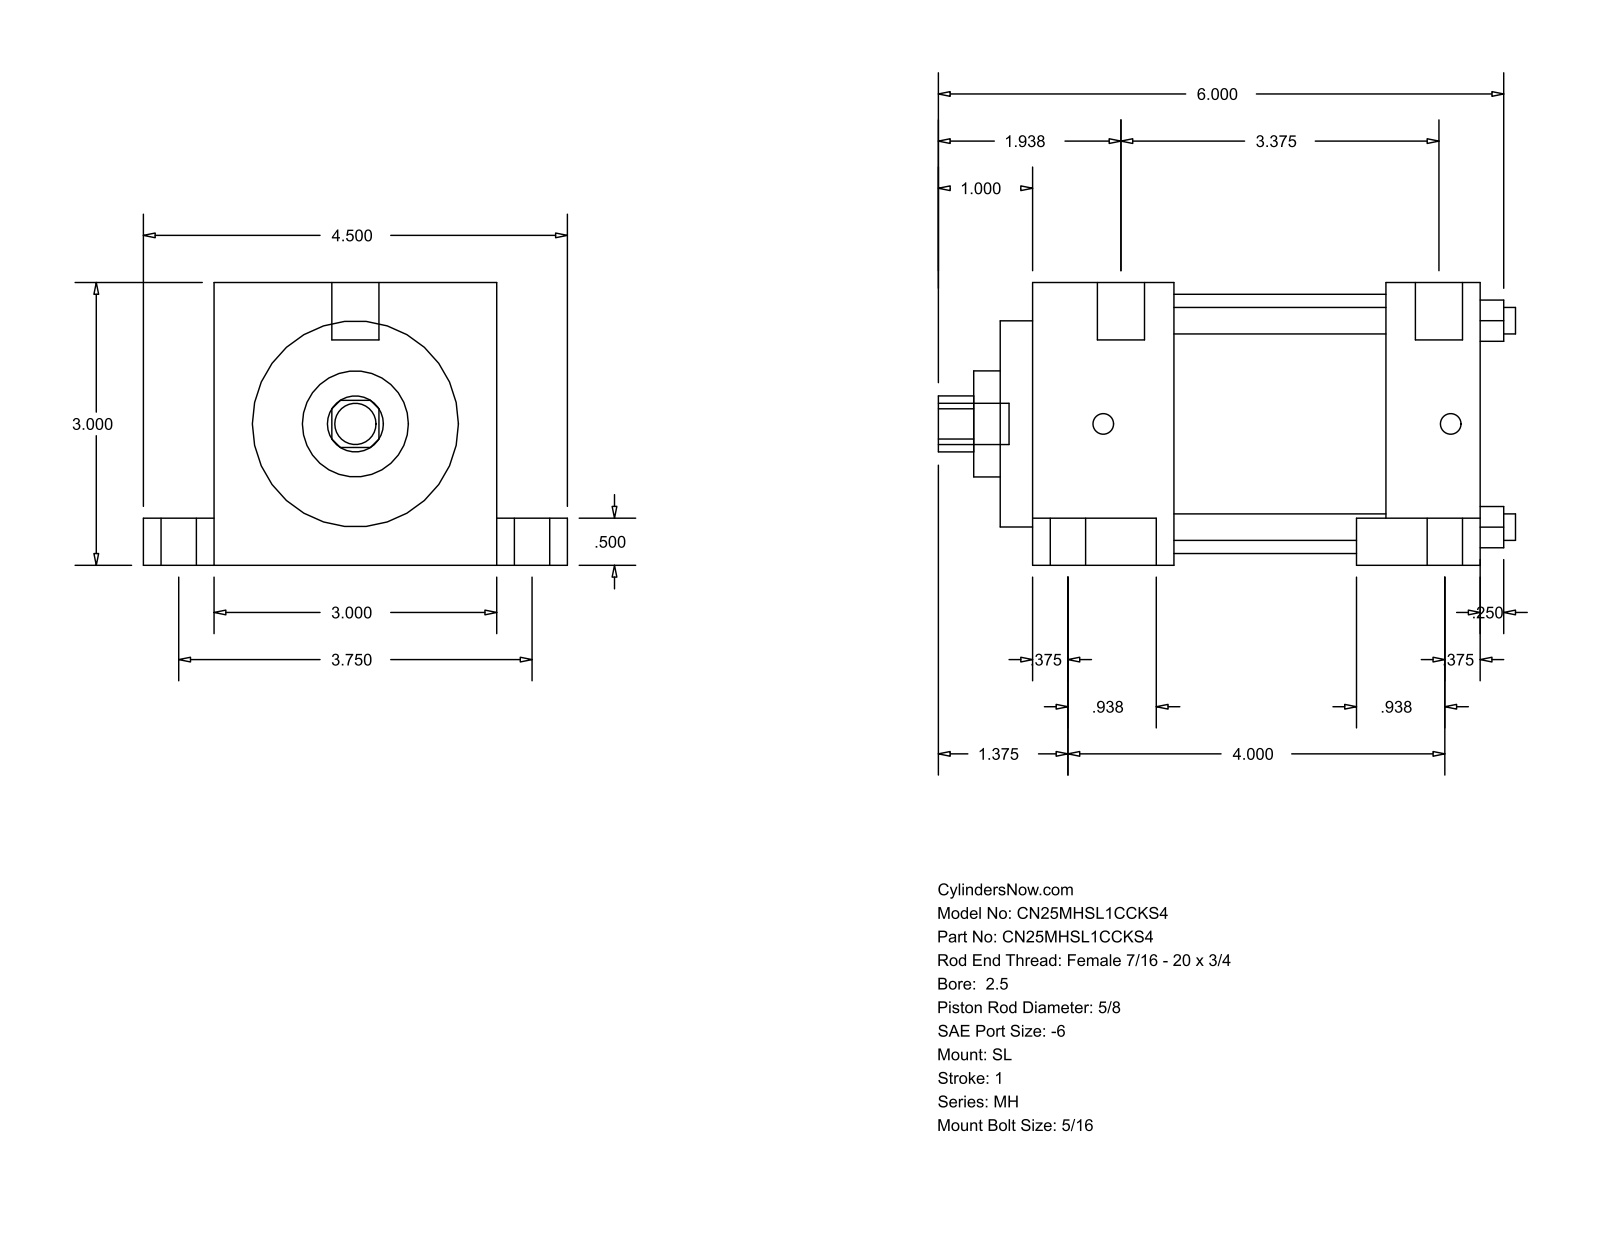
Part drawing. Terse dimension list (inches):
name: MH_SL__0250_0.625
written by: GSSL Pune (CONFIG_CONTROL_DESIGN)
unit: in
bodies: 0 solids, 86 faces (61 planar, 25 cylindrical, 0 other)
size: 6.125 × 4.5 × 3
holes: 4× ⌀0.281, 1× ⌀0.625, 1× ⌀1.125, 1× ⌀2.187, 1× ⌀2.75
bosses: 2× ⌀0.625, 2× ⌀0.375, 2× ⌀0.219, 1× ⌀0.5, 1× ⌀0.437
rounds: 1× R0.297
face distances: 3, 1, 4.094, 5.094, 0.5, 2.5, 0.75, 3.75, 5.375, 1.25
hole spacings: 1.548, 2.19, 3.097
